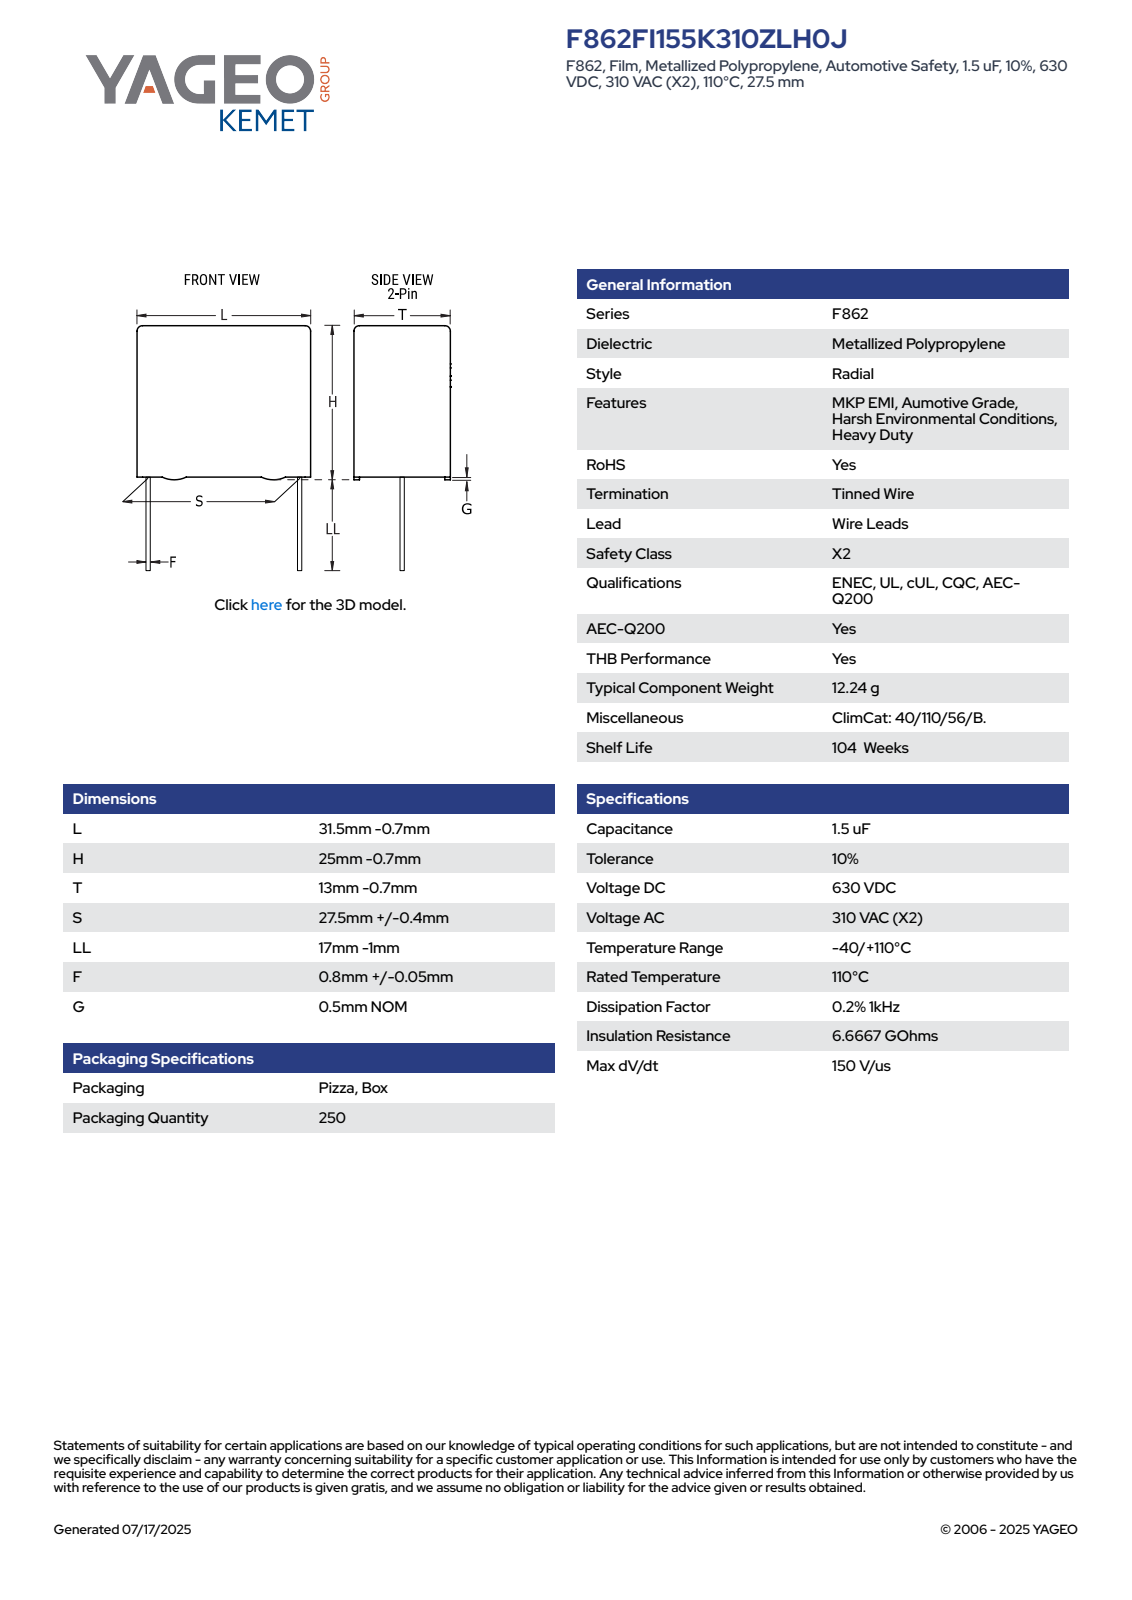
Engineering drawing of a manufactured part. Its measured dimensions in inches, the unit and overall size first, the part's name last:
Units: inches
Overall size (bounding box): 1.587 × 1.213 × 0.484
Round bosses / shafts (diameter × count): ⌀0.033 ×2
Partial cylindrical surfaces — rounded edges, fillets, slot ends (radius × count): R0.02 ×4
Main face-to-face distances: 0.484, 0.937, 1.213, 0.02, 0.957, 0.028, 0.457, 0.429, 0.63, 0.65
Volume: 0.552 in³ · Surface area: 4.655 in²
Bodies: 4 solids, 89 faces (81 planar, 8 cylindrical, 0 other)
Part name (STEP PRODUCT): CFR_RBG_31.5X25X13_L30.8H24.3T12.3S27.5LL16F0.85G0.5
STEP written by: SolidWorks 2014 (AUTOMOTIVE_DESIGN)
